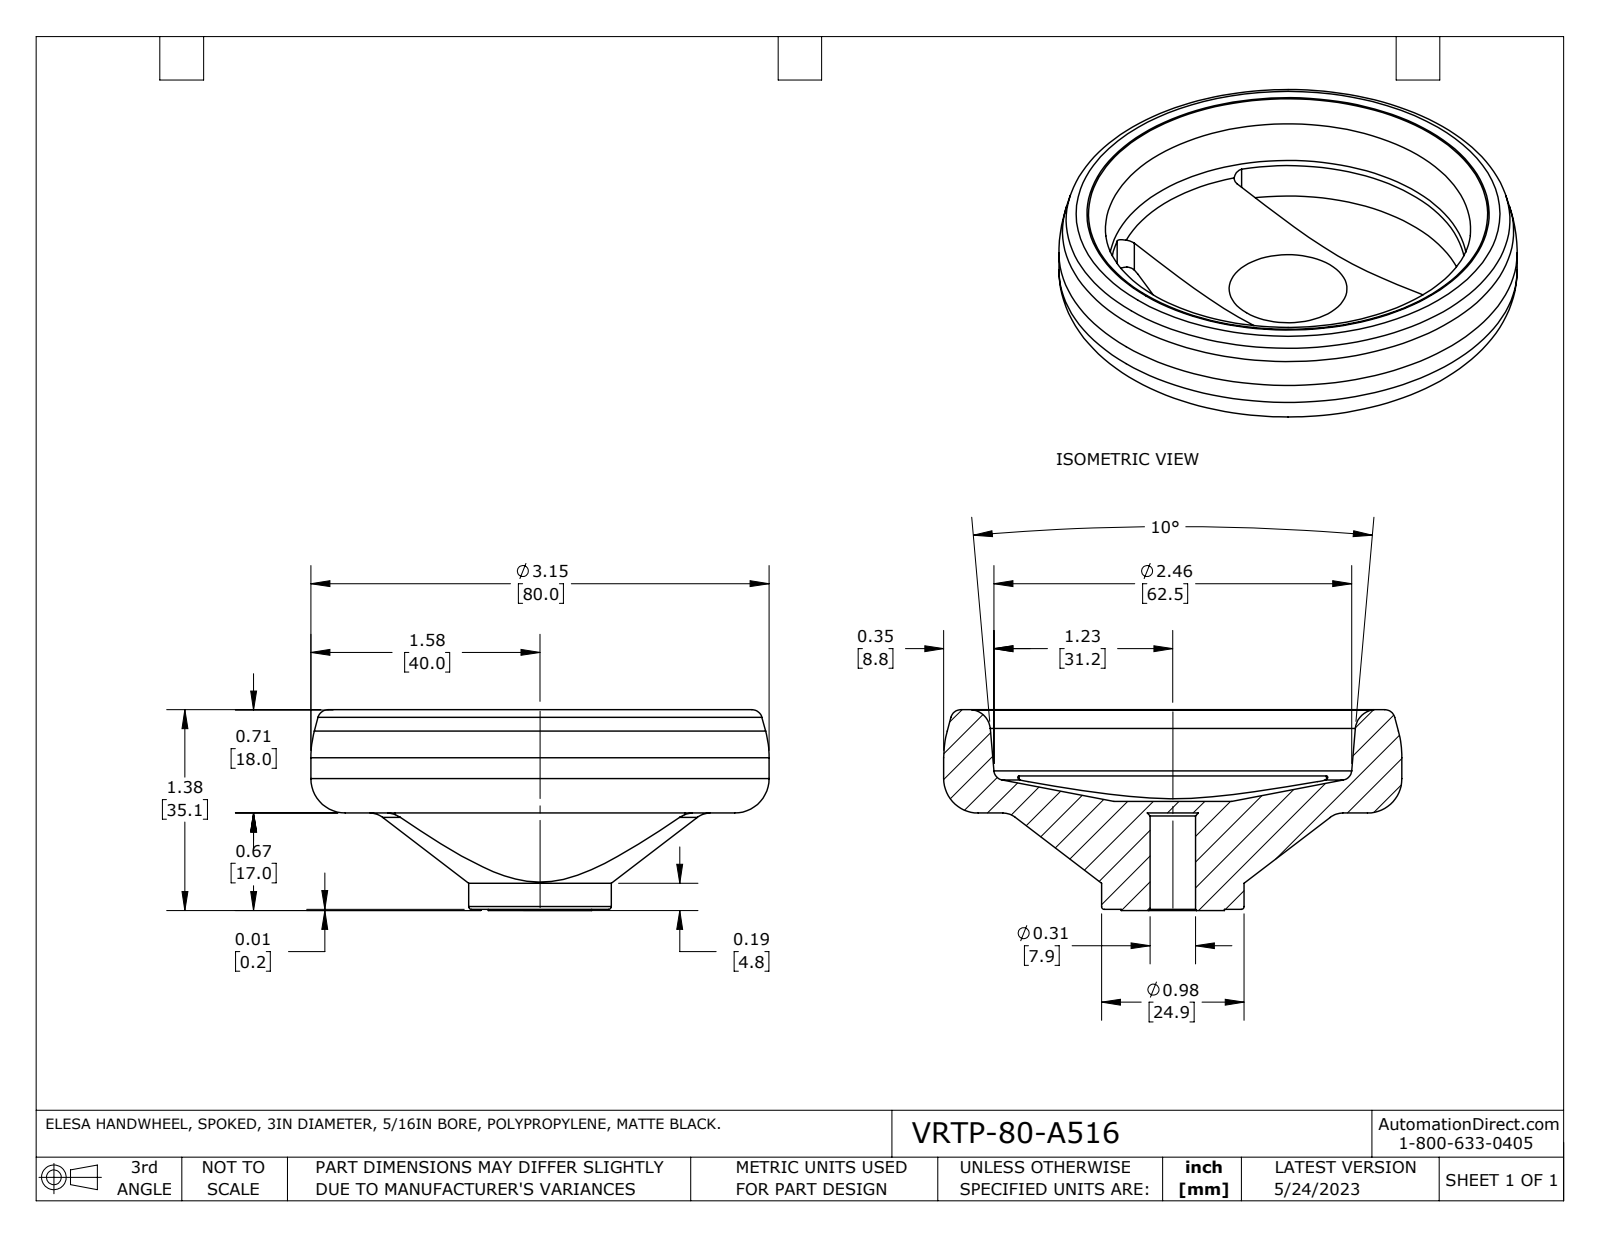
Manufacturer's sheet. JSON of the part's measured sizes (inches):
{"part_name": "VRTP-80-A516", "step_written_by": "SolidWorks 2021 (AUTOMOTIVE_DESIGN)", "units": "inches", "bodies": {"solids": 1, "faces": 33, "planar": 8, "cylindrical": 10, "other": 15}, "overall_size": [3.15, 3.15, 1.38], "volume_in3": 3.047, "surface_area_in2": 23.98, "round_holes": [[0.312, 1]], "round_bosses_or_shafts": [[3.15, 1], [0.98, 1], [0.71, 1]], "partial_cylinders_radius": [[0.07, 4], [1.217, 1]], "face_to_face_distances": [0.999, 0.71, 0.08, 0.63, 0.67, 0.75, 1.38, 0.662, 0.742, 1.372]}
